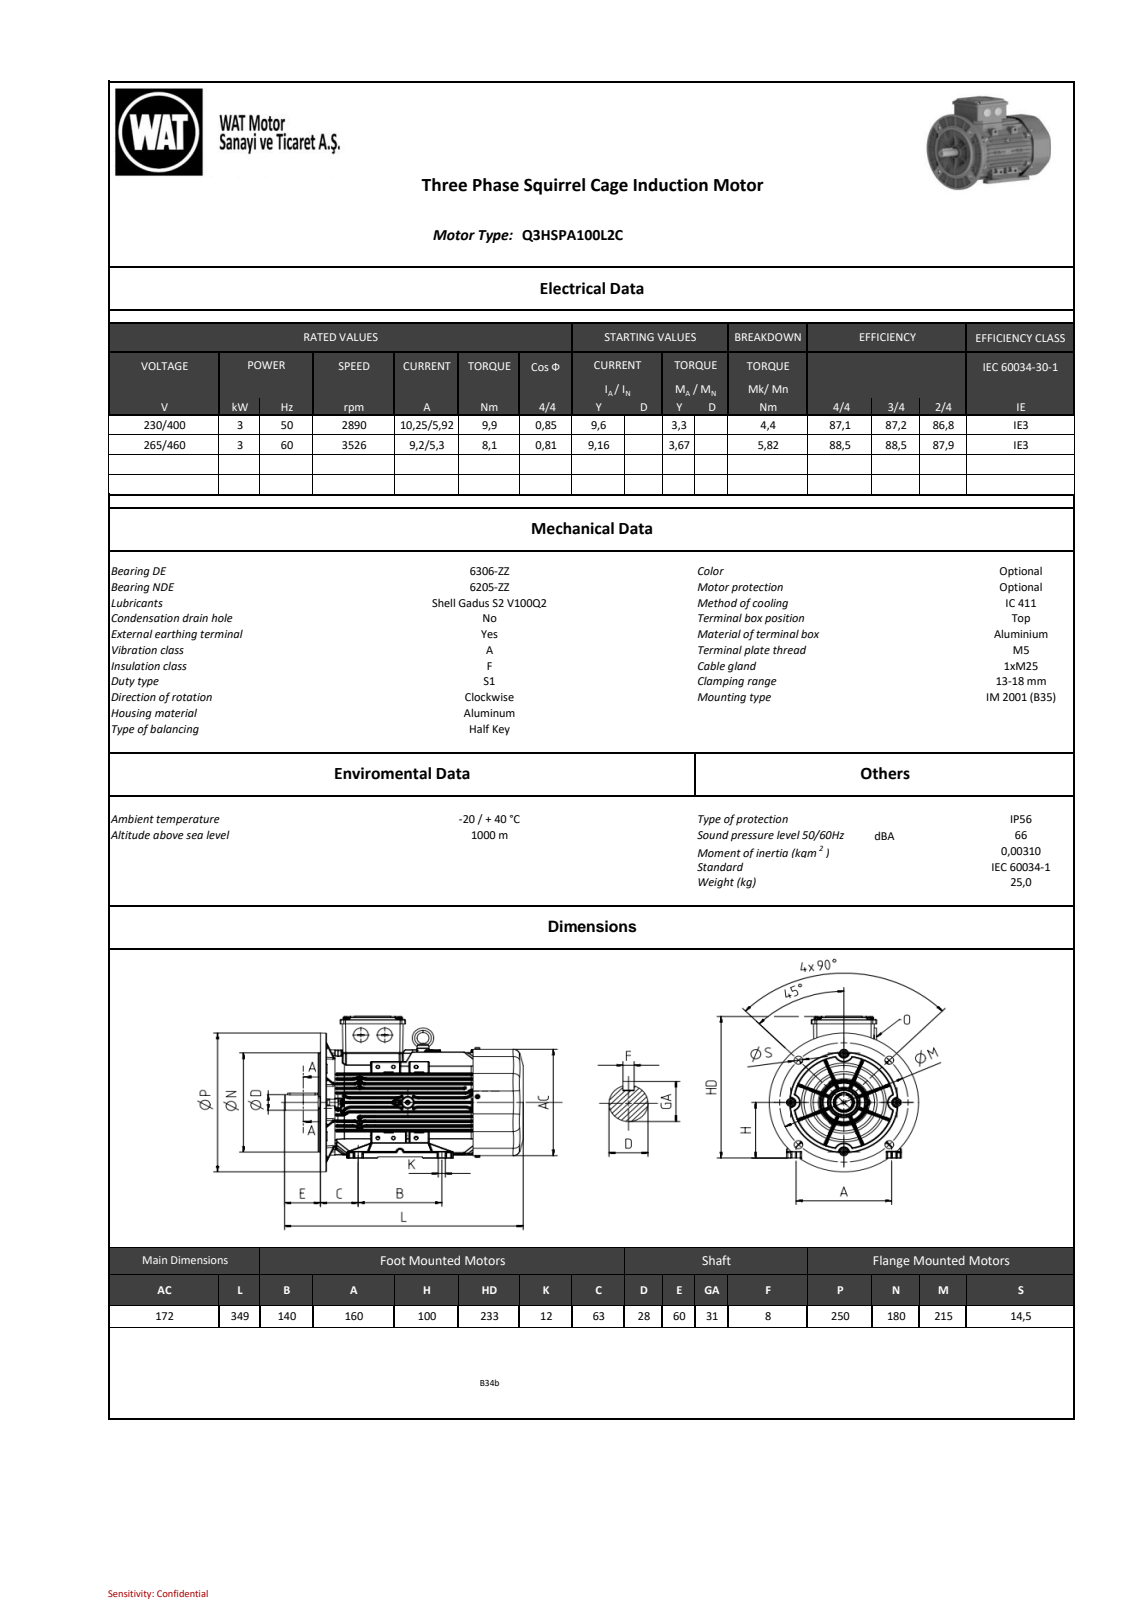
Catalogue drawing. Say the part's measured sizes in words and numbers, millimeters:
The part is named "QHS series_ 100_B35_stp_objects". Its 3-D file was written by "SIEMENS PLM Software NX2206.8101 (AUTOMOTIVE_DESIGN)". It is 0 solids with 6732 faces: 1645 planar, 2936 cylindrical and 2151 other. Overall it measures 349.04 by 258.21 by 250.32 millimeters. Round holes: 4 of diameter 11, 1 of diameter 8.5, 1 of diameter 9.87, 1 of diameter 10.5, 1 of diameter 79.79, 1 of diameter 97.79, 1 of diameter 115.78. Round bosses or shafts: 7 of diameter 8, 7 of diameter 5, 4 of diameter 9.5, 2 of diameter 25, 1 of diameter 180, 1 of diameter 102.19, 1 of diameter 84.19, 1 of diameter 30. Partial cylindrical surfaces (rounded edges, fillets, slot ends): 857 of radius 1, 638 of radius 0.8, 263 of radius 0.5, 69 of radius 2, 28 of radius 8, 11 of radius 1.5, 10 of radius 4, 8 of radius 1.6. The main face-to-face distances are 4, 7.5, 91.91, 16, 8.93, 82.98, 23.57, 222, 206, 7.37. The hole center spacings are 79.4, 112.29, 158.8, 79.25, 79.55.
